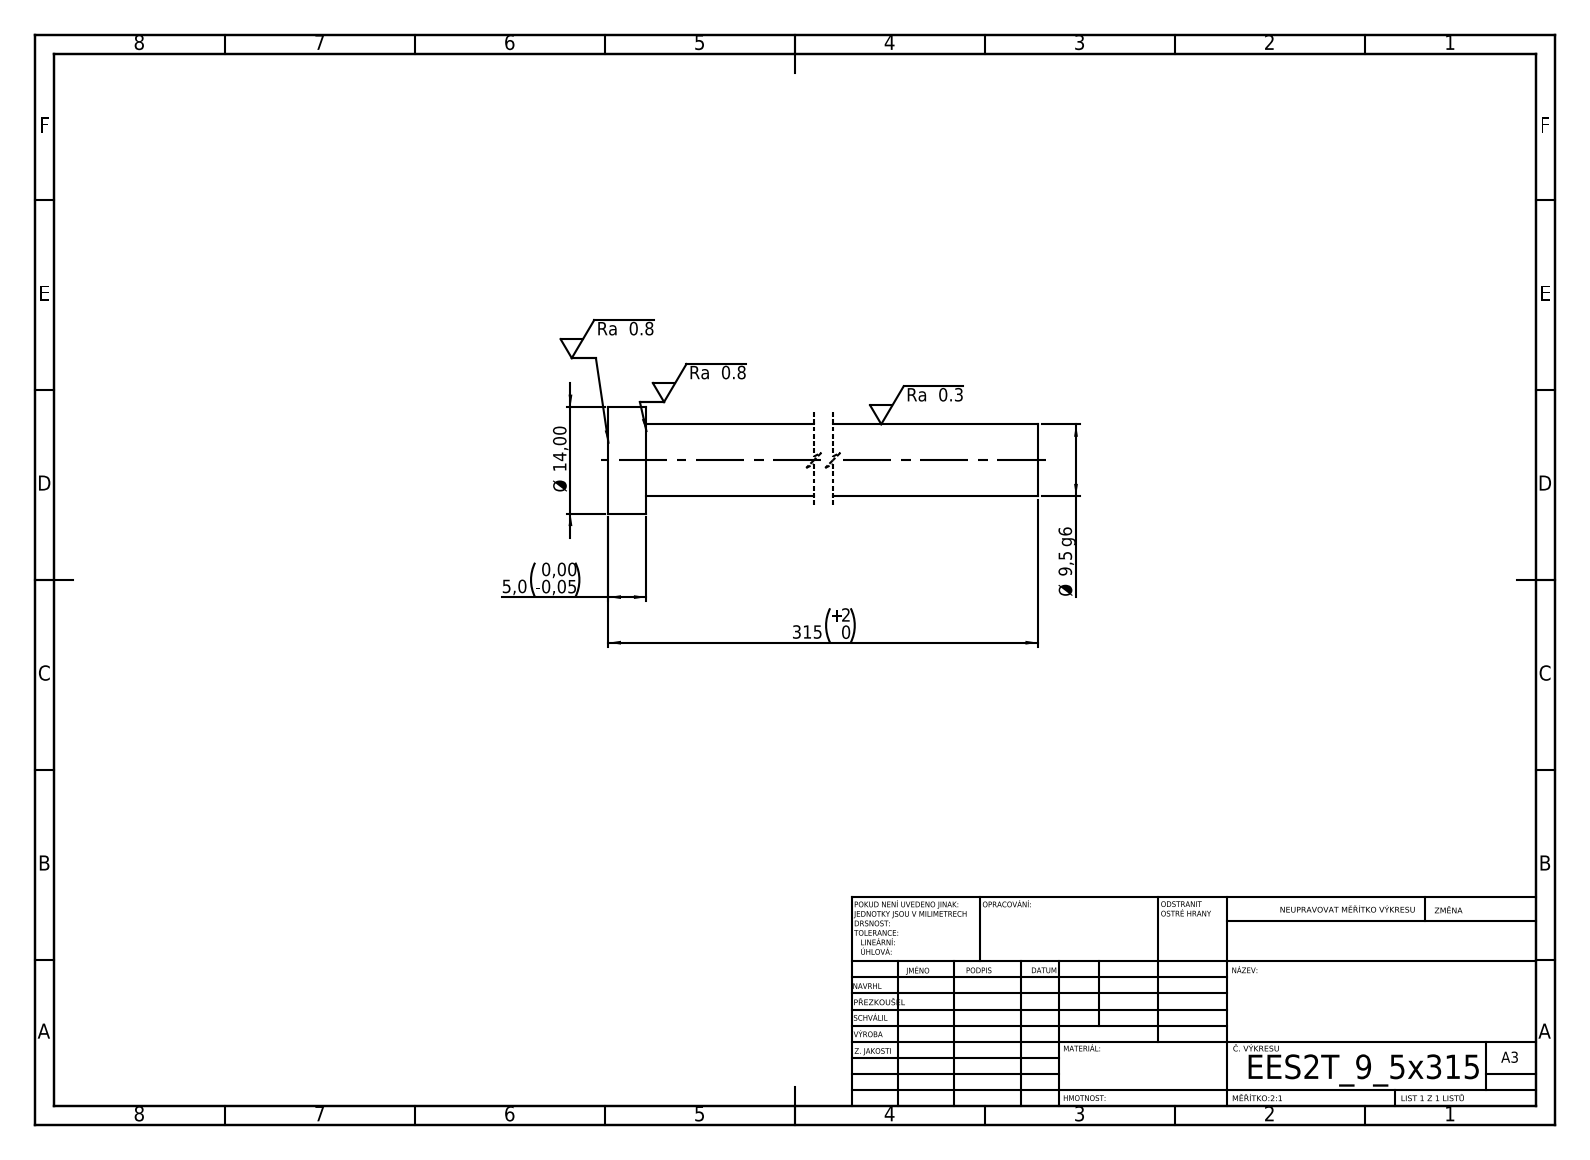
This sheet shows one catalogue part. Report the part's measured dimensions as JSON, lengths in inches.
{"step_written_by": "SolidWorks 2019 (CONFIG_CONTROL_DESIGN)", "units": "inches", "bodies": {"solids": 1, "faces": 7, "planar": 3, "cylindrical": 4, "other": 0}, "overall_size": [12.402, 0.551, 0.551], "volume_in3": 1.388, "surface_area_in2": 15.16, "round_bosses_or_shafts": [[0.551, 1], [0.374, 1]], "face_to_face_distances": [0.197, 12.402, 12.205]}
